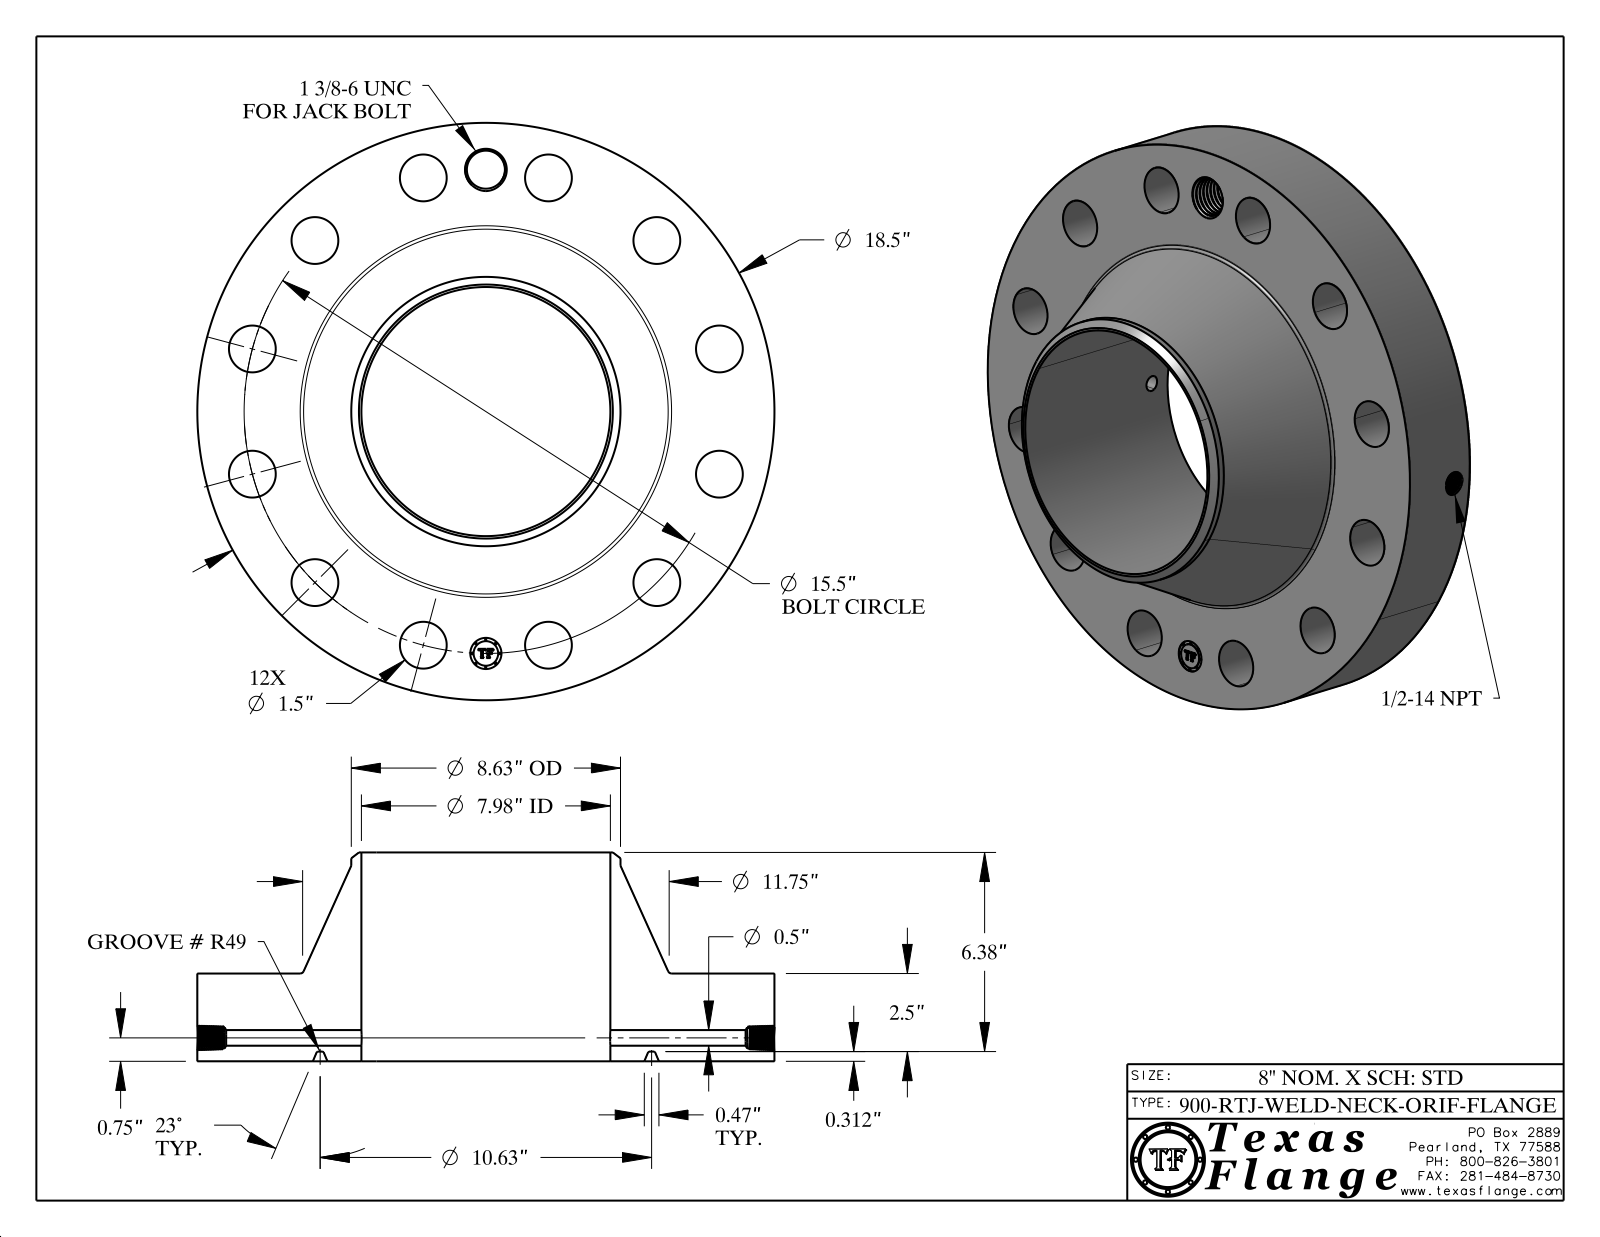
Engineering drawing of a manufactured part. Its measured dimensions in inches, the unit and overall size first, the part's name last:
Units: inches
Overall size (bounding box): 18.5 × 18.5 × 6.692
Round holes (diameter × count): ⌀1.5 ×12, ⌀0.5 ×1, ⌀0.672 ×1, ⌀1 ×1, ⌀1.219 ×1, ⌀7.981 ×1
Round bosses / shafts (diameter × count): ⌀0.061 ×8, ⌀18.5 ×1, ⌀8.63 ×1, ⌀0.788 ×1
Main face-to-face distances: 2.812, 0.312, 2.5, 6.692, 6.38, 3.88, 2.797, 2.485, 0.015, 3.895
Hole centre spacings: 7.75, 13.423, 14.972, 4.011, 7.75, 10.96, 15.5, 2.023
Volume: 660 in³ · Surface area: 1 011 in²
Bodies: 1 solid, 796 faces (370 planar, 103 cylindrical, 323 other)
Part name (STEP PRODUCT): 900-RTJ-WELD-NECK
STEP written by: CATIA V5 STEP AP214 (AUTOMOTIVE_DESIGN)
